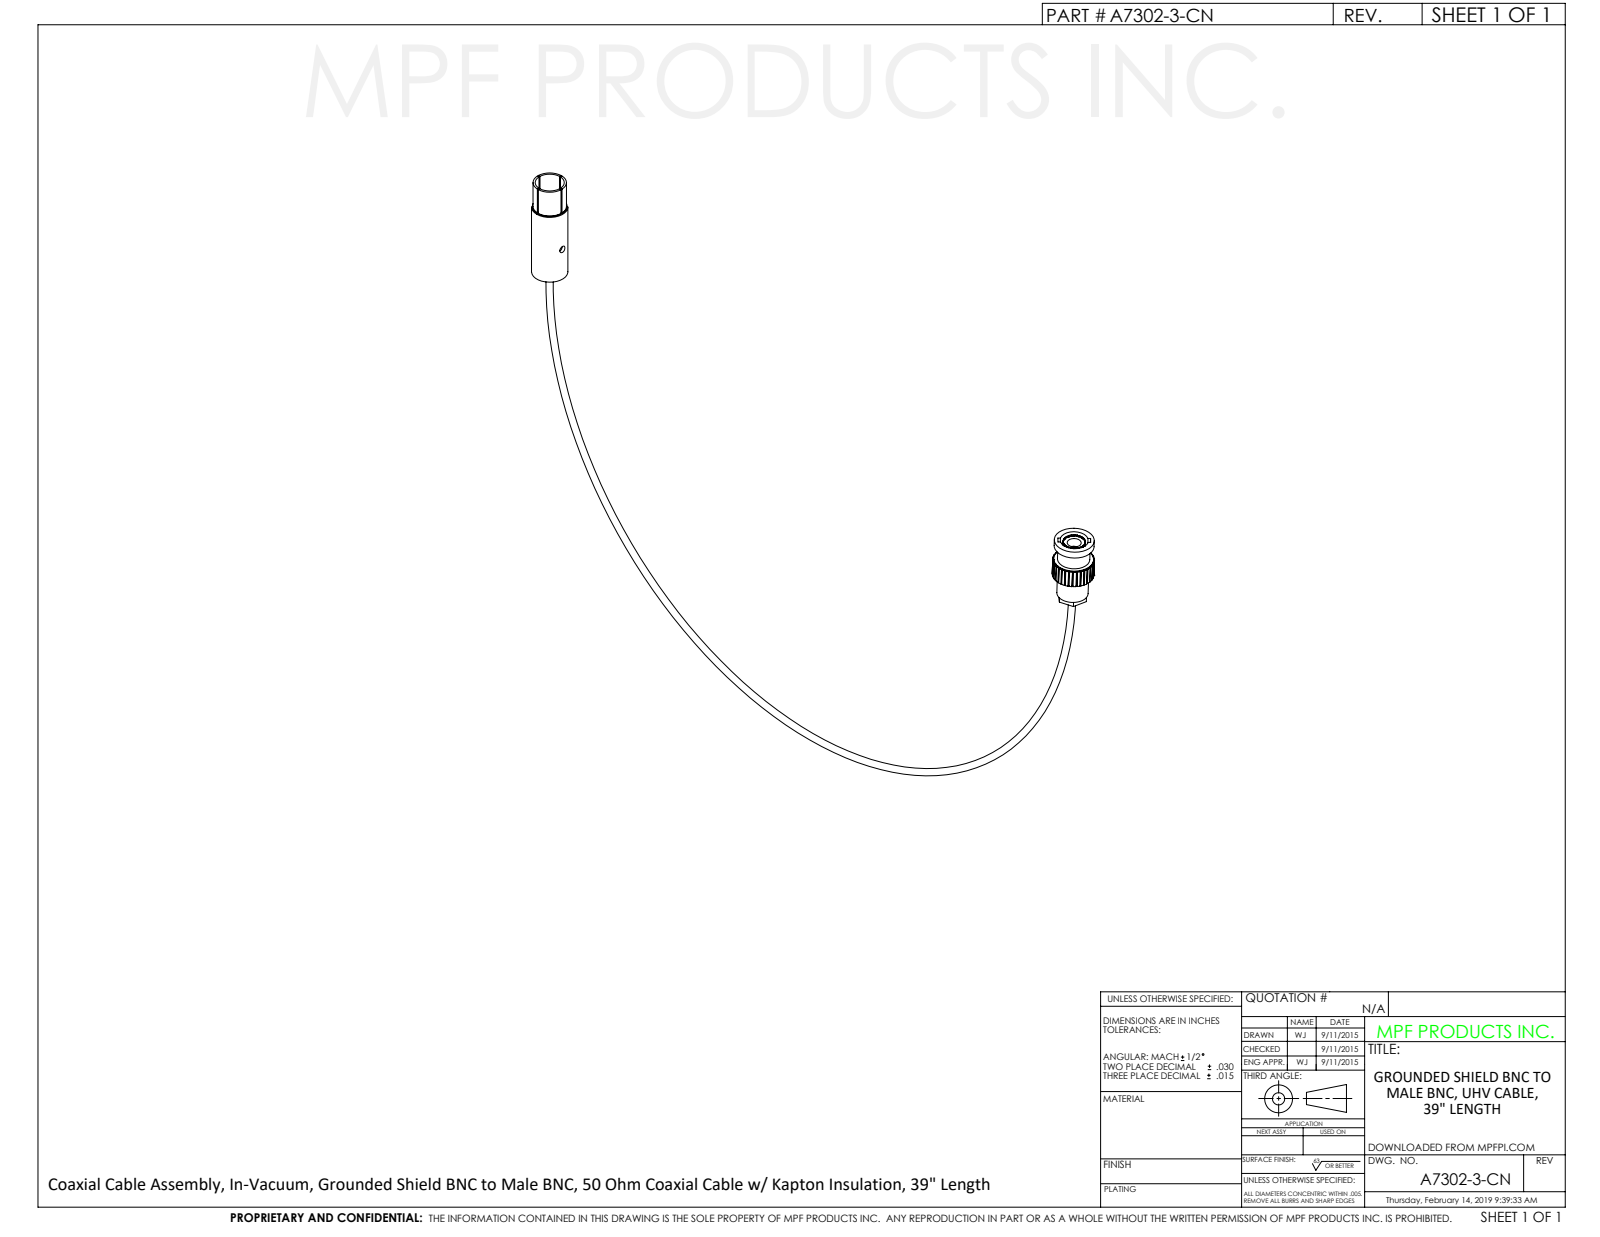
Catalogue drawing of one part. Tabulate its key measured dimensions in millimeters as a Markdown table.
| quantity | value |
| --- | --- |
| part name | A7302-3-CN |
| STEP written by | SolidWorks 2012 (CONFIG_CONTROL_DESIGN) |
| units | millimeters |
| bodies | 2 solids, 338 faces (235 planar, 98 cylindrical, 5 other) |
| overall size | 275.5 × 173.6 × 19.1 |
| volume | 10 600 mm³ |
| surface area | 9 903 mm² |
| round holes (diameter × count) | 2.5 × 2, 1.9 × 1, 4 × 1, 4.9 × 1, 9.9 × 1, 12.7 × 1 |
| round bosses / shafts (diameter × count) | 19.1 × 1, 18 × 1, 14 × 1, 13.3 × 1, 11.3 × 1, 10.9 × 1, 7.8 × 1 |
| partial cylindrical surfaces (radius × count) | 1.7 × 1, 3.8 × 1, 3.8 × 1, 7.3 × 1 |
| main face-to-face distances | 38.1, 5.1, 33, 0.5, 8.3, 24.8, 0.4, 16.6, 22.3, 5.7 |
